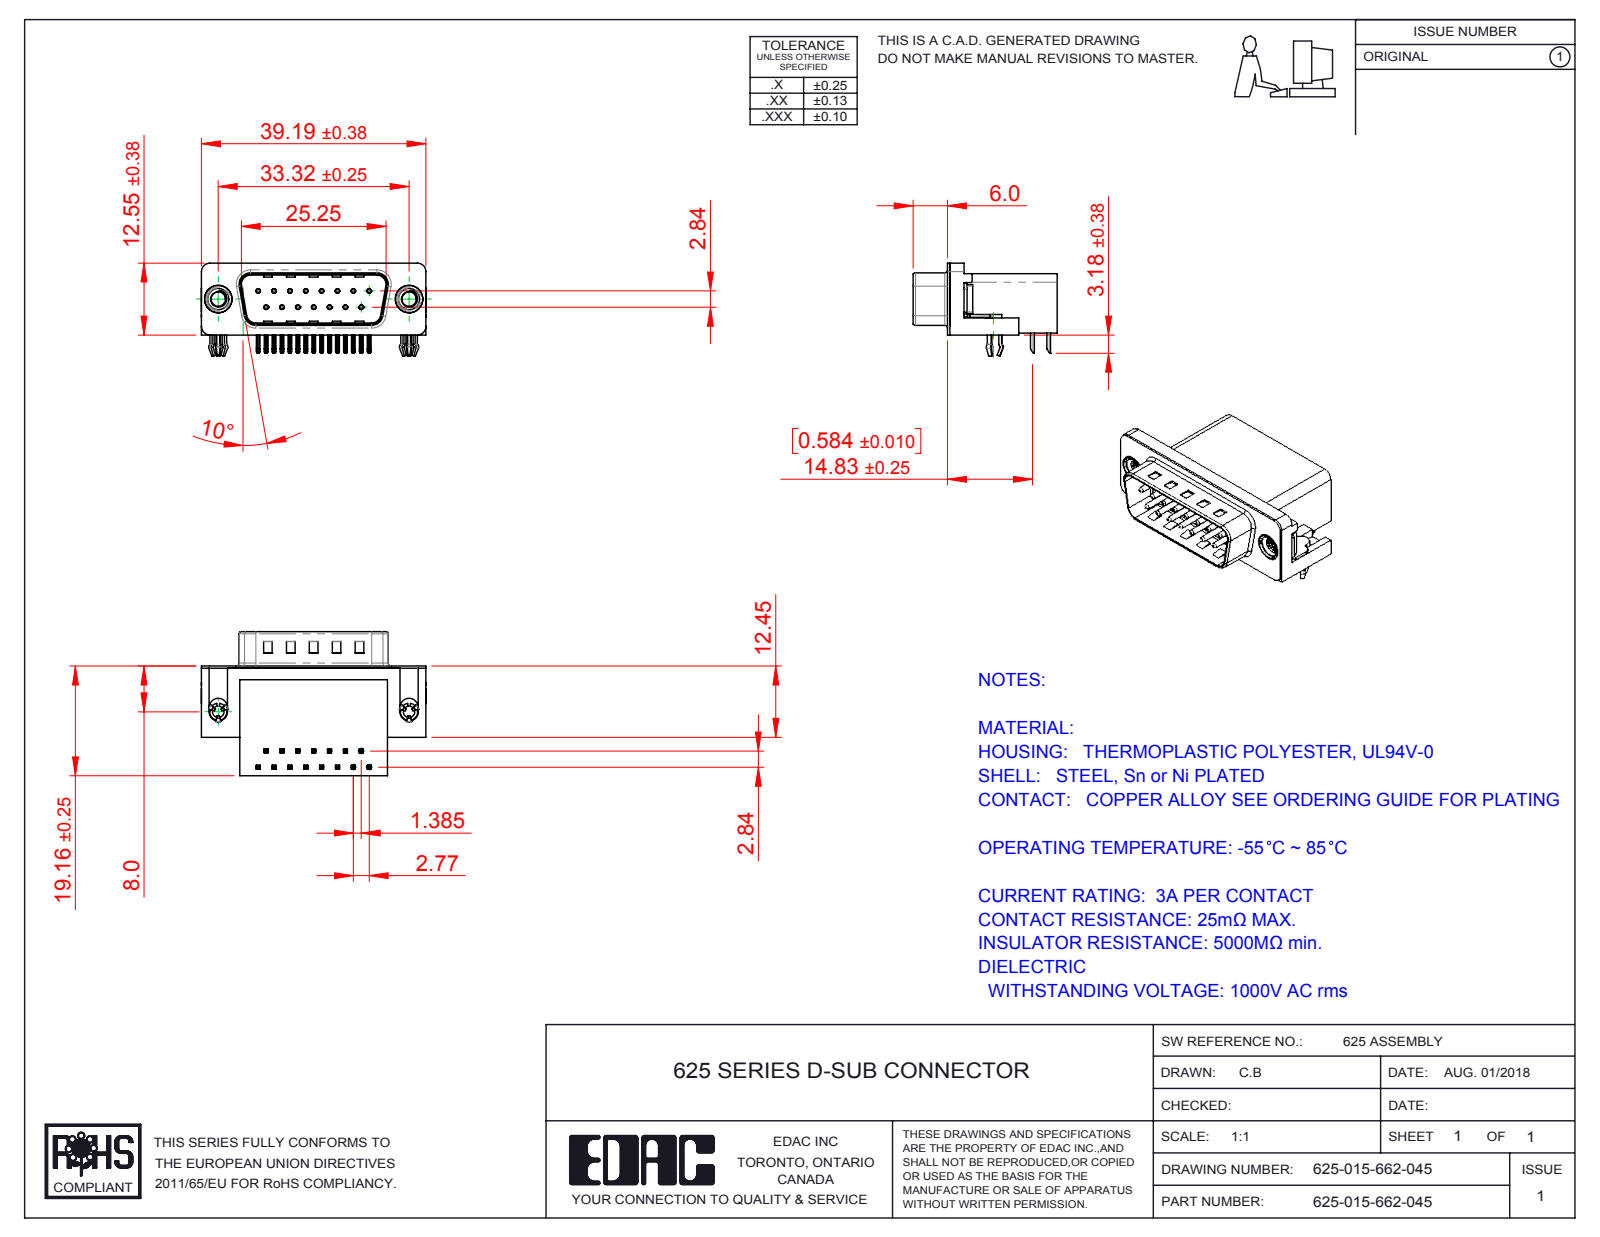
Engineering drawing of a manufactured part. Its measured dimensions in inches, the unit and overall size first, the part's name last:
Units: inches
Overall size (bounding box): 1.544 × 0.991 × 0.64
Round holes (diameter × count): ⌀0.014 ×15, ⌀0.031 ×15, ⌀0.079 ×2, ⌀0.098 ×2, ⌀0.157 ×2, ⌀0.189 ×2, ⌀0.197 ×2
Round bosses / shafts (diameter × count): ⌀0.03 ×15, ⌀0.193 ×2, ⌀0.187 ×2, ⌀0.154 ×2, ⌀0.118 ×2
Partial cylindrical surfaces — rounded edges, fillets, slot ends (radius × count): R0.01 ×72, R0.005 ×30, R0.039 ×16, R0.02 ×9, R0.063 ×8, R0.059 ×6, R0.035 ×4, R0.079 ×4
Main face-to-face distances: 0.016, 0.407, 0.739, 0.083, 0.412, 0.754, 0.067, 0.428, 0.345, 0.64
Hole centre spacings: 0.124, 0.109, 0.218, 0.327, 0.436, 0.198, 0.198, 0.294
Volume: 0.381 in³ · Surface area: 10.06 in²
Bodies: 21 solids, 1583 faces (931 planar, 457 cylindrical, 195 other)
Part name (STEP PRODUCT): 625 Contact Top; 625 Housing_15 Socket; 625-015-662-045; 625 M3 Threaded Rivet (+3 more)
STEP written by: SolidWorks 2016 (CONFIG_CONTROL_DESIGN)
